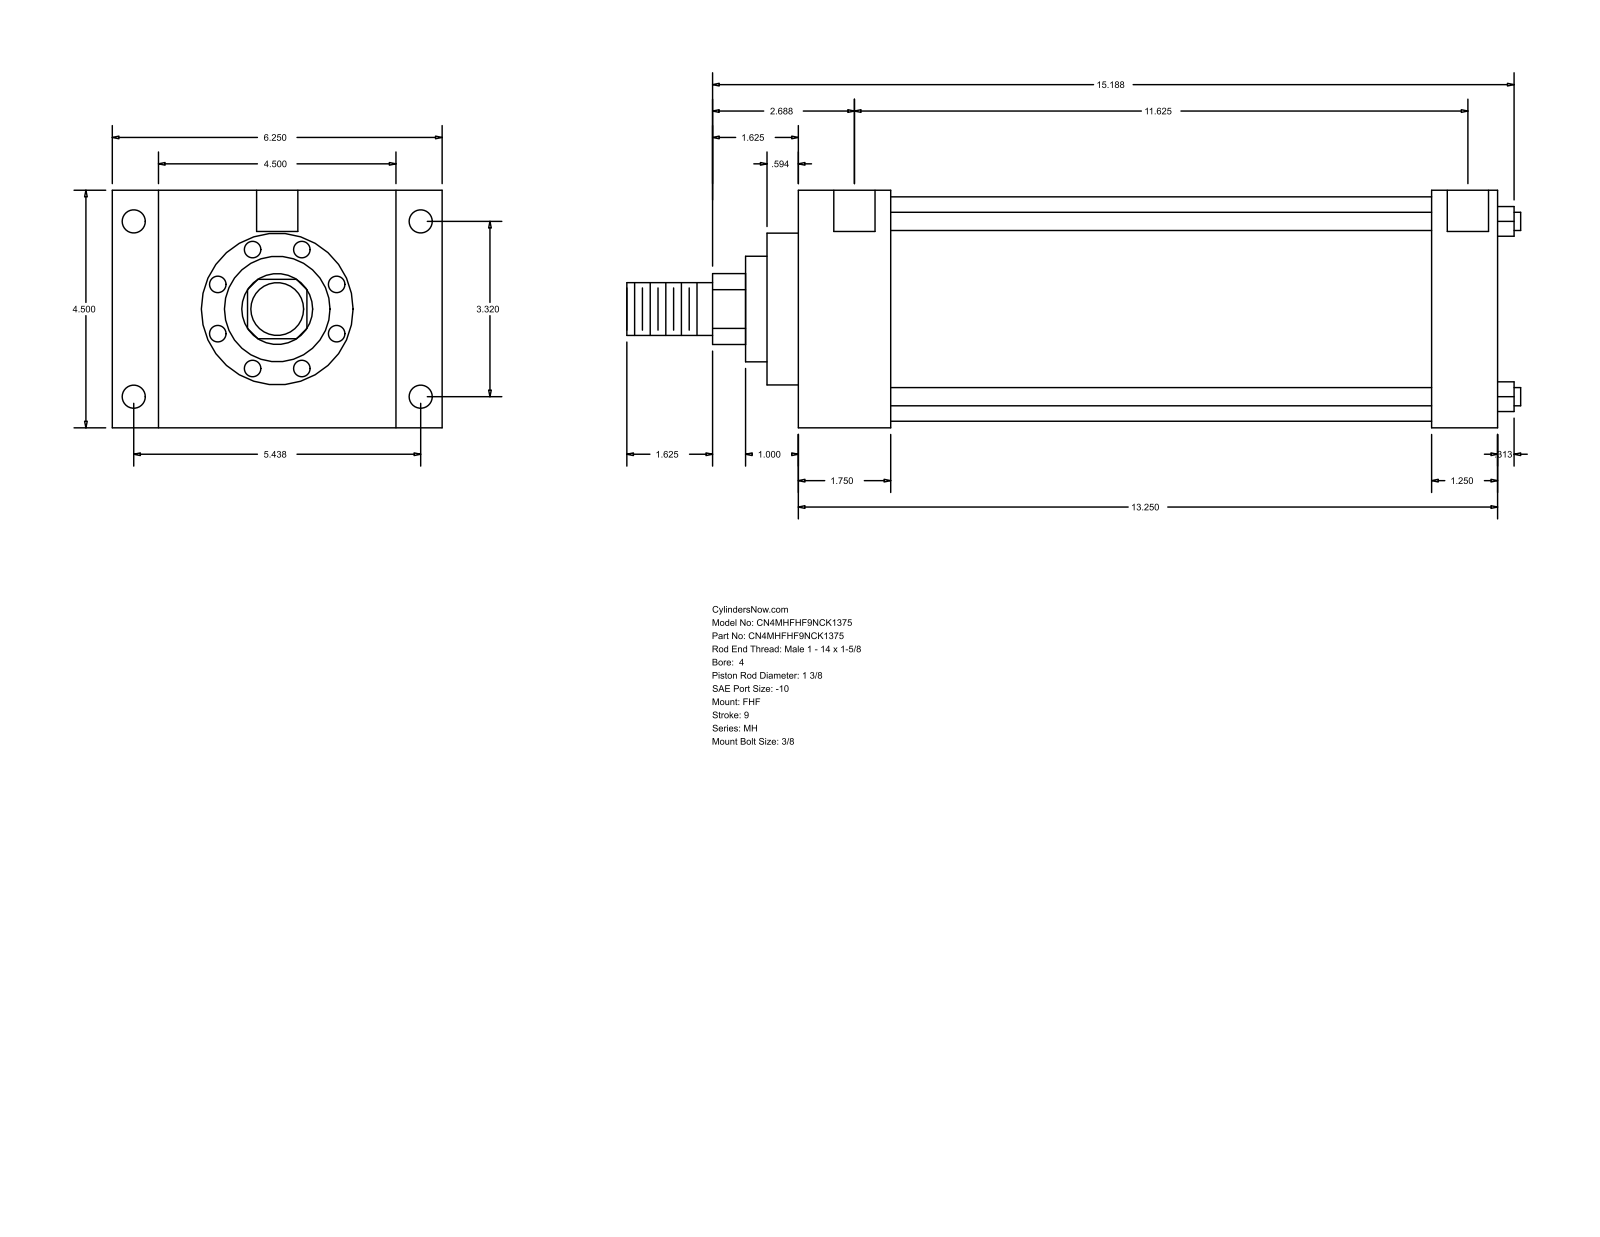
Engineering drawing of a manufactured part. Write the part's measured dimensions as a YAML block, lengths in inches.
part_name: "MH_FHF__0400_1.375"
step_written_by: "GSSL Pune (CONFIG_CONTROL_DESIGN)"
units: inches
bodies: {solids: 0, faces: 90, planar: 61, cylindrical: 29, other: 0}
overall_size: [16.937, 6.25, 4.5]
round_holes:
  - {diameter: 0.344, count: 4}
  - {diameter: 0.438, count: 4}
  - {diameter: 0.781, count: 2}
round_bosses_or_shafts:
  - {diameter: 0.345, count: 4}
  - {diameter: 4.25, count: 1}
  - {diameter: 2.875, count: 1}
  - {diameter: 2, count: 1}
  - {diameter: 1.375, count: 1}
  - {diameter: 1, count: 1}
partial_cylinders:
  - {radius: 0.672, count: 1}
face_to_face_distances: [4.5, 13.25, 1.75, 11.5, 0.875, 5.375, 6.25, 12, 10.25, 1.25]
hole_center_spacings: [3.32, 5.438, 6.371, 11.75, 0.062, 0.063, 11.625, 11.687]
